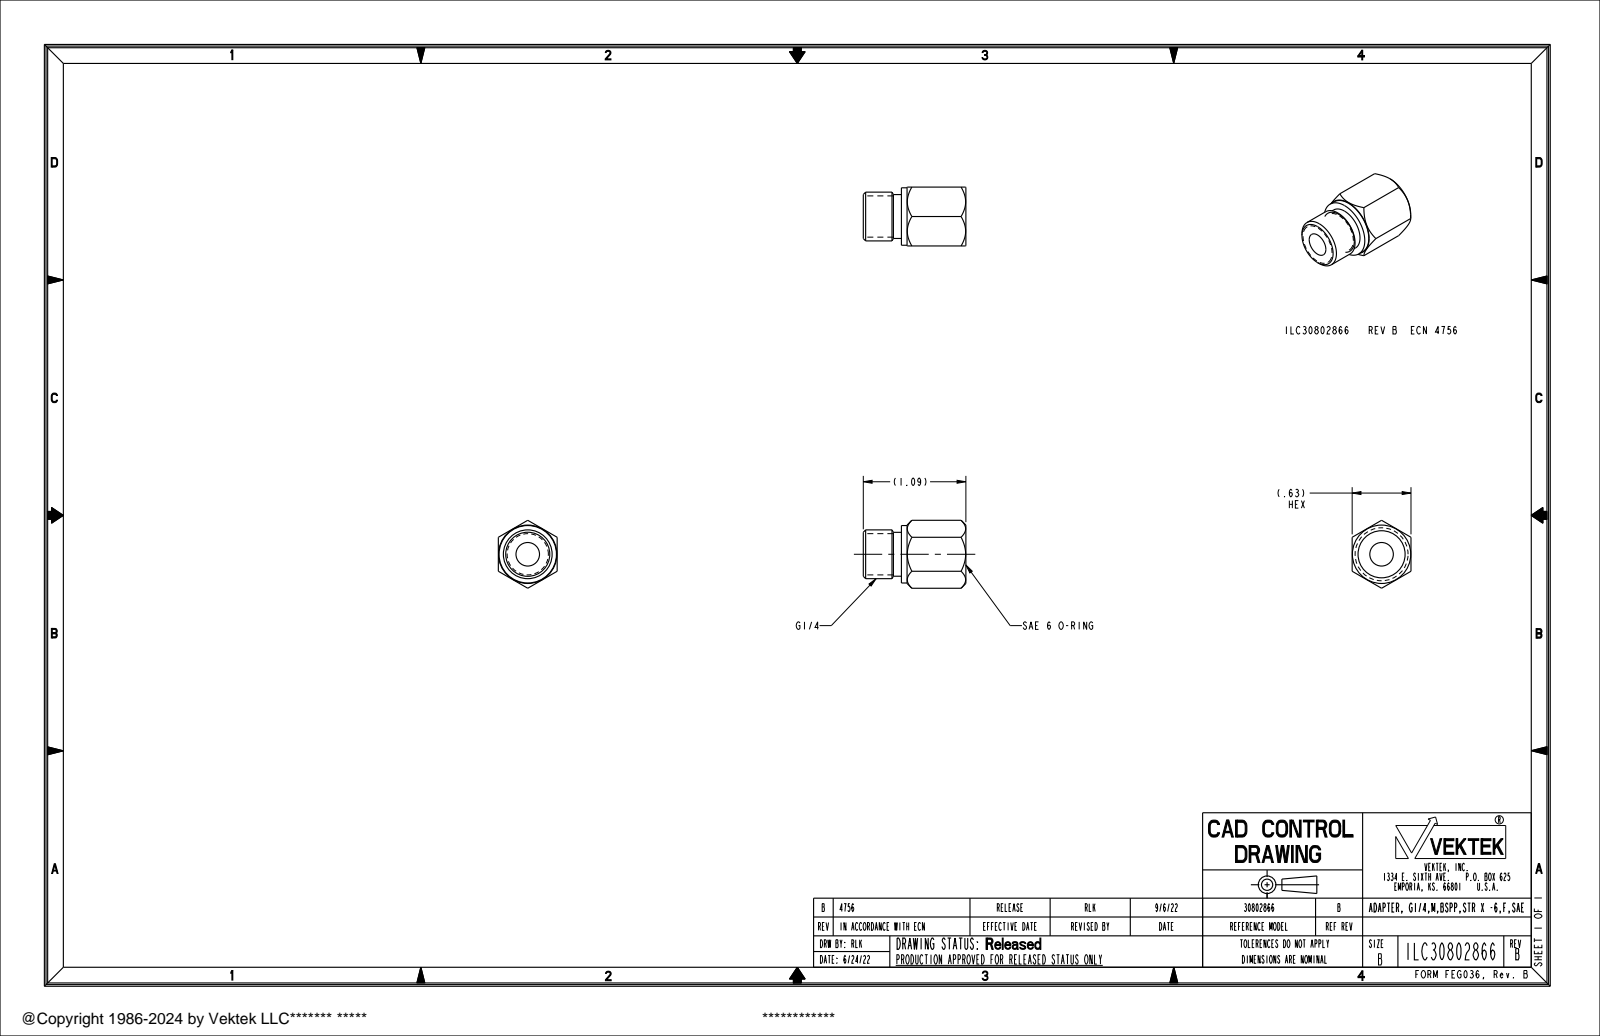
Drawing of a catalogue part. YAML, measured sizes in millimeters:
part_name: "ILC30802866"
step_written_by: "CREO PARAMETRIC BY PTC INC, 2021164 (AUTOMOTIVE_DESIGN)"
units: millimeters
bodies: {solids: 1, faces: 36, planar: 12, cylindrical: 14, other: 10}
overall_size: [27.7, 18.3, 15.9]
volume: 2900
surface_area: 3229
round_holes:
  - {diameter: 6.4, count: 1}
  - {diameter: 12.7, count: 1}
round_bosses_or_shafts:
  - {diameter: 15.5, count: 1}
  - {diameter: 14.3, count: 1}
  - {diameter: 13.2, count: 1}
  - {diameter: 11.8, count: 1}
  - {diameter: 11.1, count: 1}
face_to_face_distances: [15.9, 10.3, 17.4, 27.7, 8.6, 8.8, 19.1, 19.6, 10.9, 2.2]
